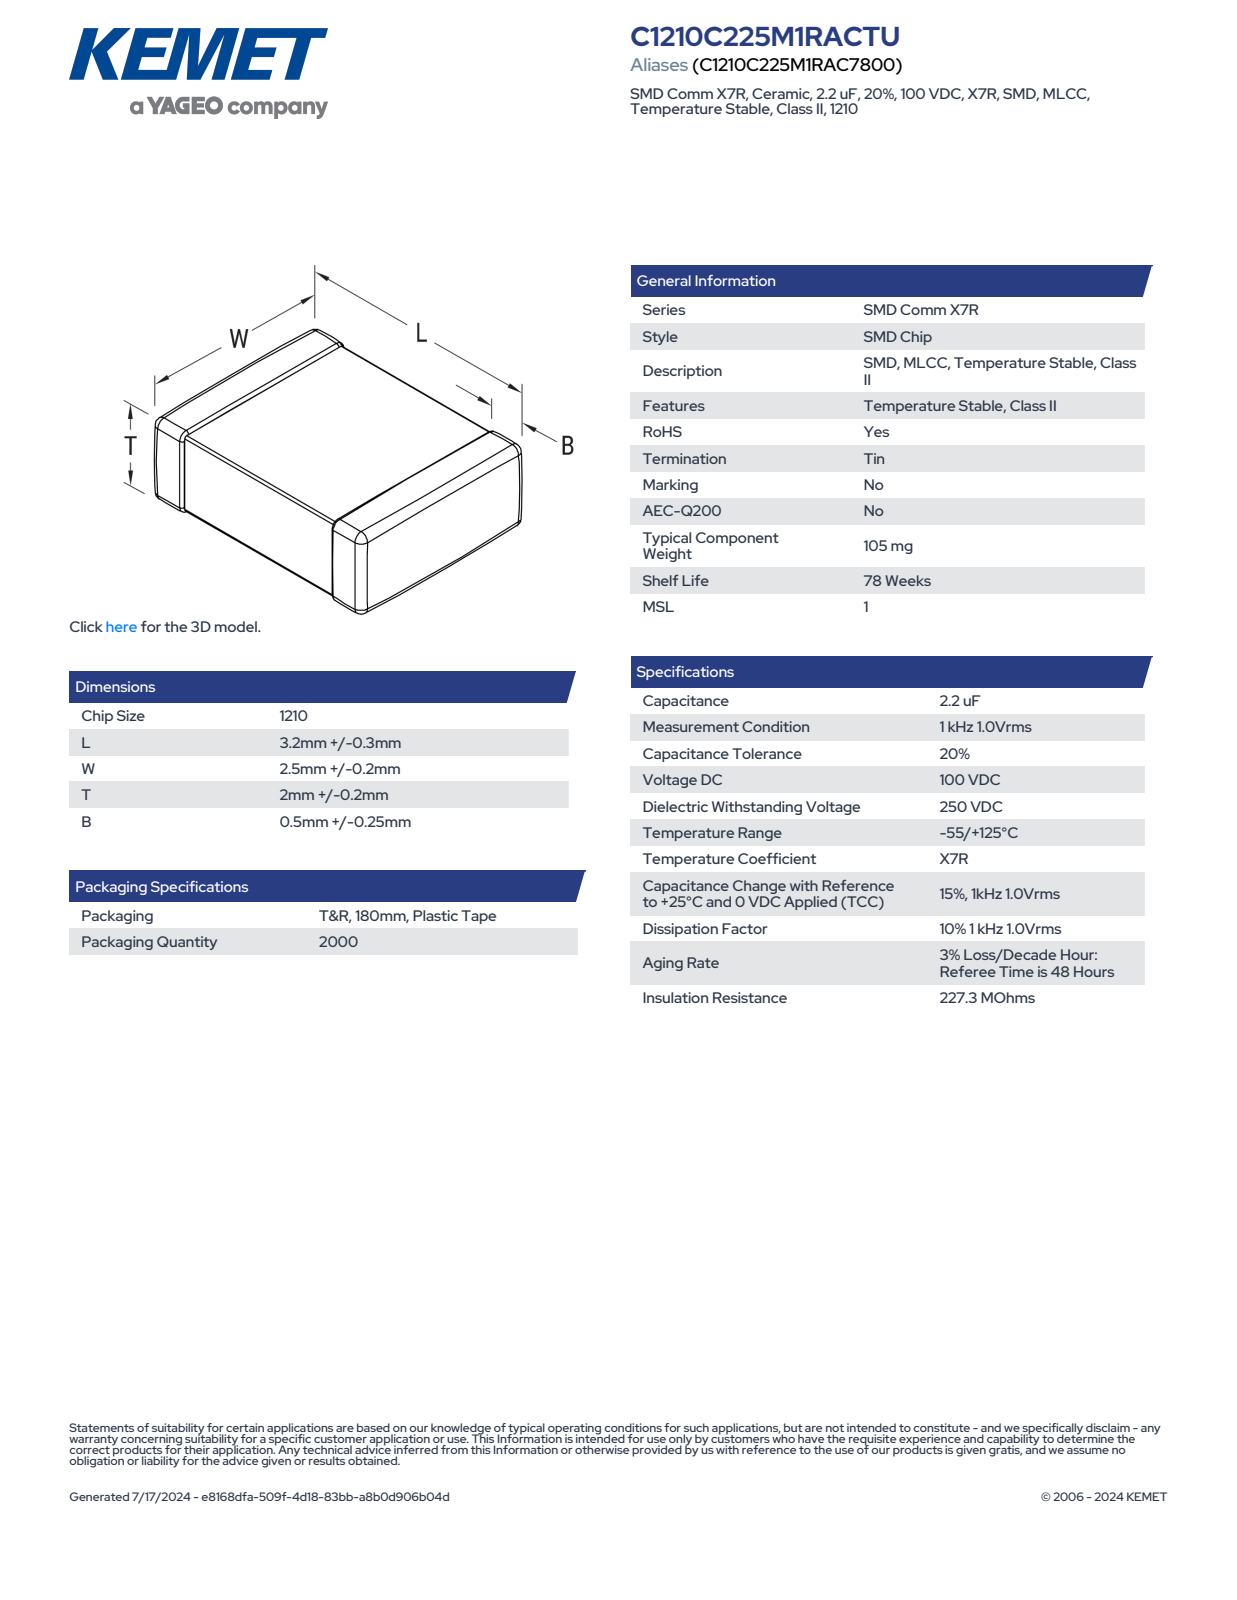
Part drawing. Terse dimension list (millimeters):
name: CCS_CCSTD_1210_L3.5W2.7T2.2B0.5
written by: SolidWorks 2021 (AUTOMOTIVE_DESIGN)
unit: mm
bodies: 4 solids, 125 faces (71 planar, 38 cylindrical, 16 other)
size: 3.5 × 2.7 × 2.2
volume: 20 mm³; area: 46 mm²
face distances: 2.14, 3.5, 2.64, 2.08, 2.58, 2.2, 2.7, 2.15, 2.09, 0.4
